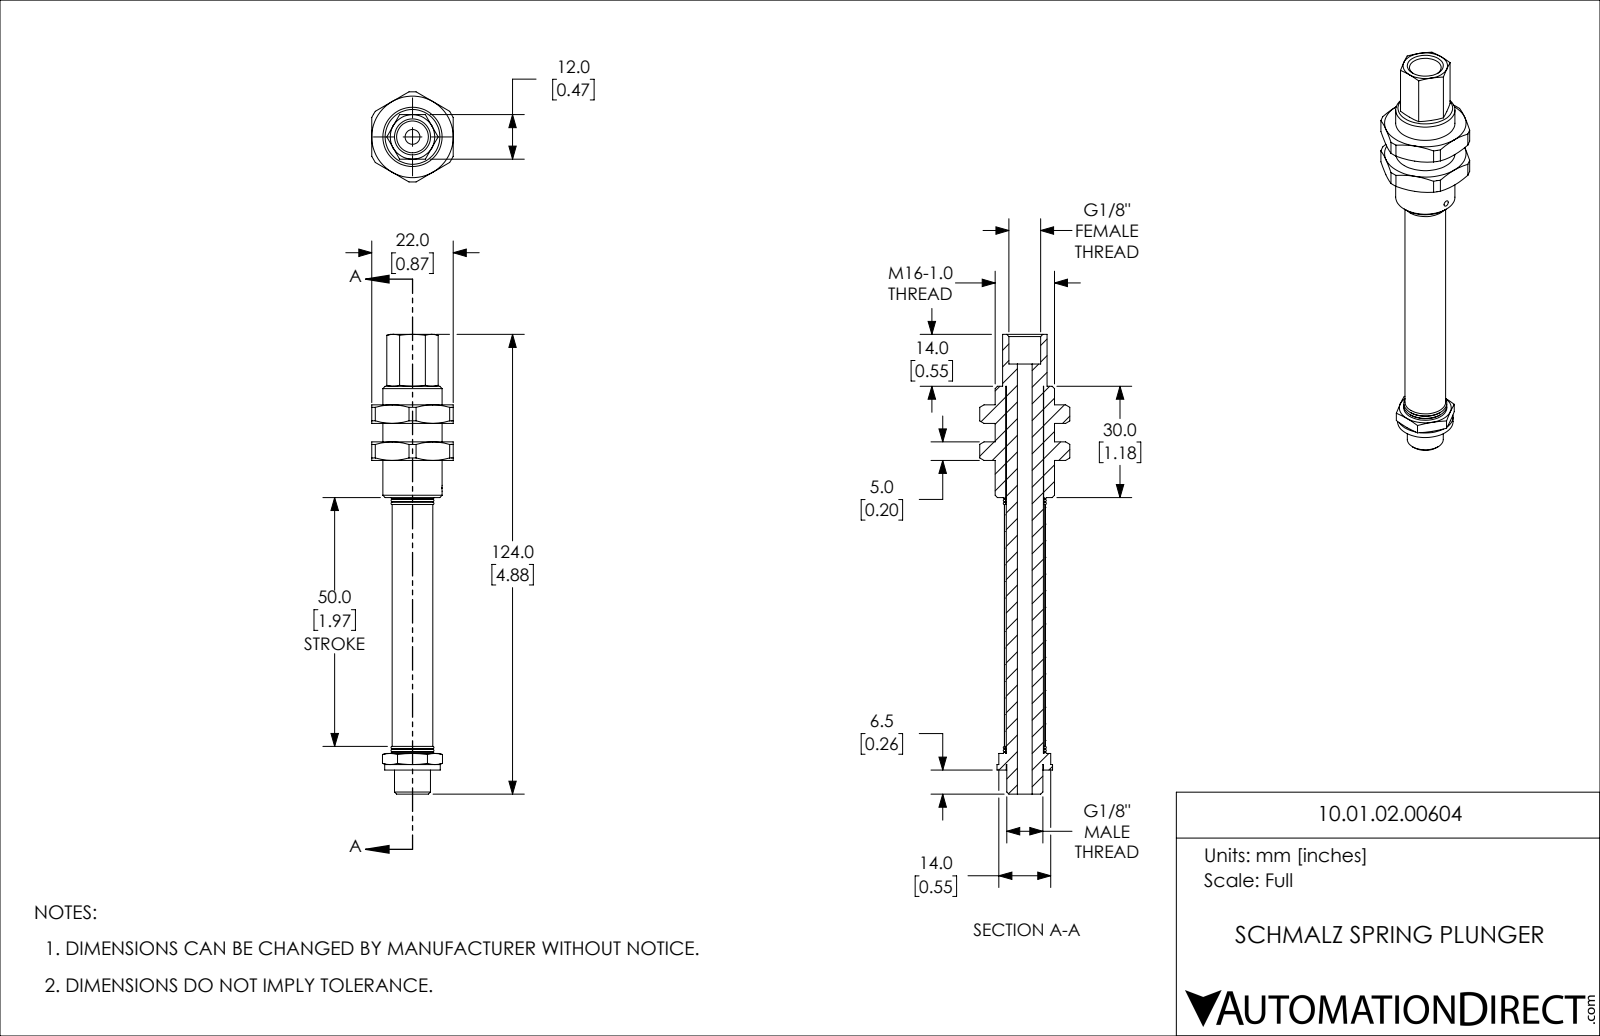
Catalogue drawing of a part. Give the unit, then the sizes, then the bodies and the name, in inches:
Units: inches
Overall size (bounding box): 4.882 × 0.957 × 0.866
Round holes (diameter × count): ⌀0.063 ×1, ⌀0.157 ×1, ⌀0.337 ×1, ⌀0.394 ×1, ⌀0.402 ×1, ⌀0.432 ×1
Round bosses / shafts (diameter × count): ⌀0.63 ×1, ⌀0.591 ×1, ⌀0.432 ×1, ⌀0.383 ×1
Main face-to-face distances: 0.197, 0.394, 0.591, 0.472, 0.866, 0.039, 0.512, 0.787, 0.551, 3.287
Volume: 0.889 in³ · Surface area: 22.91 in²
Bodies: 1 solid, 188 faces (52 planar, 42 cylindrical, 94 other)
Part name (STEP PRODUCT): 10.01.02.00604
STEP written by: SolidWorks 2021 (CONFIG_CONTROL_DESIGN)
